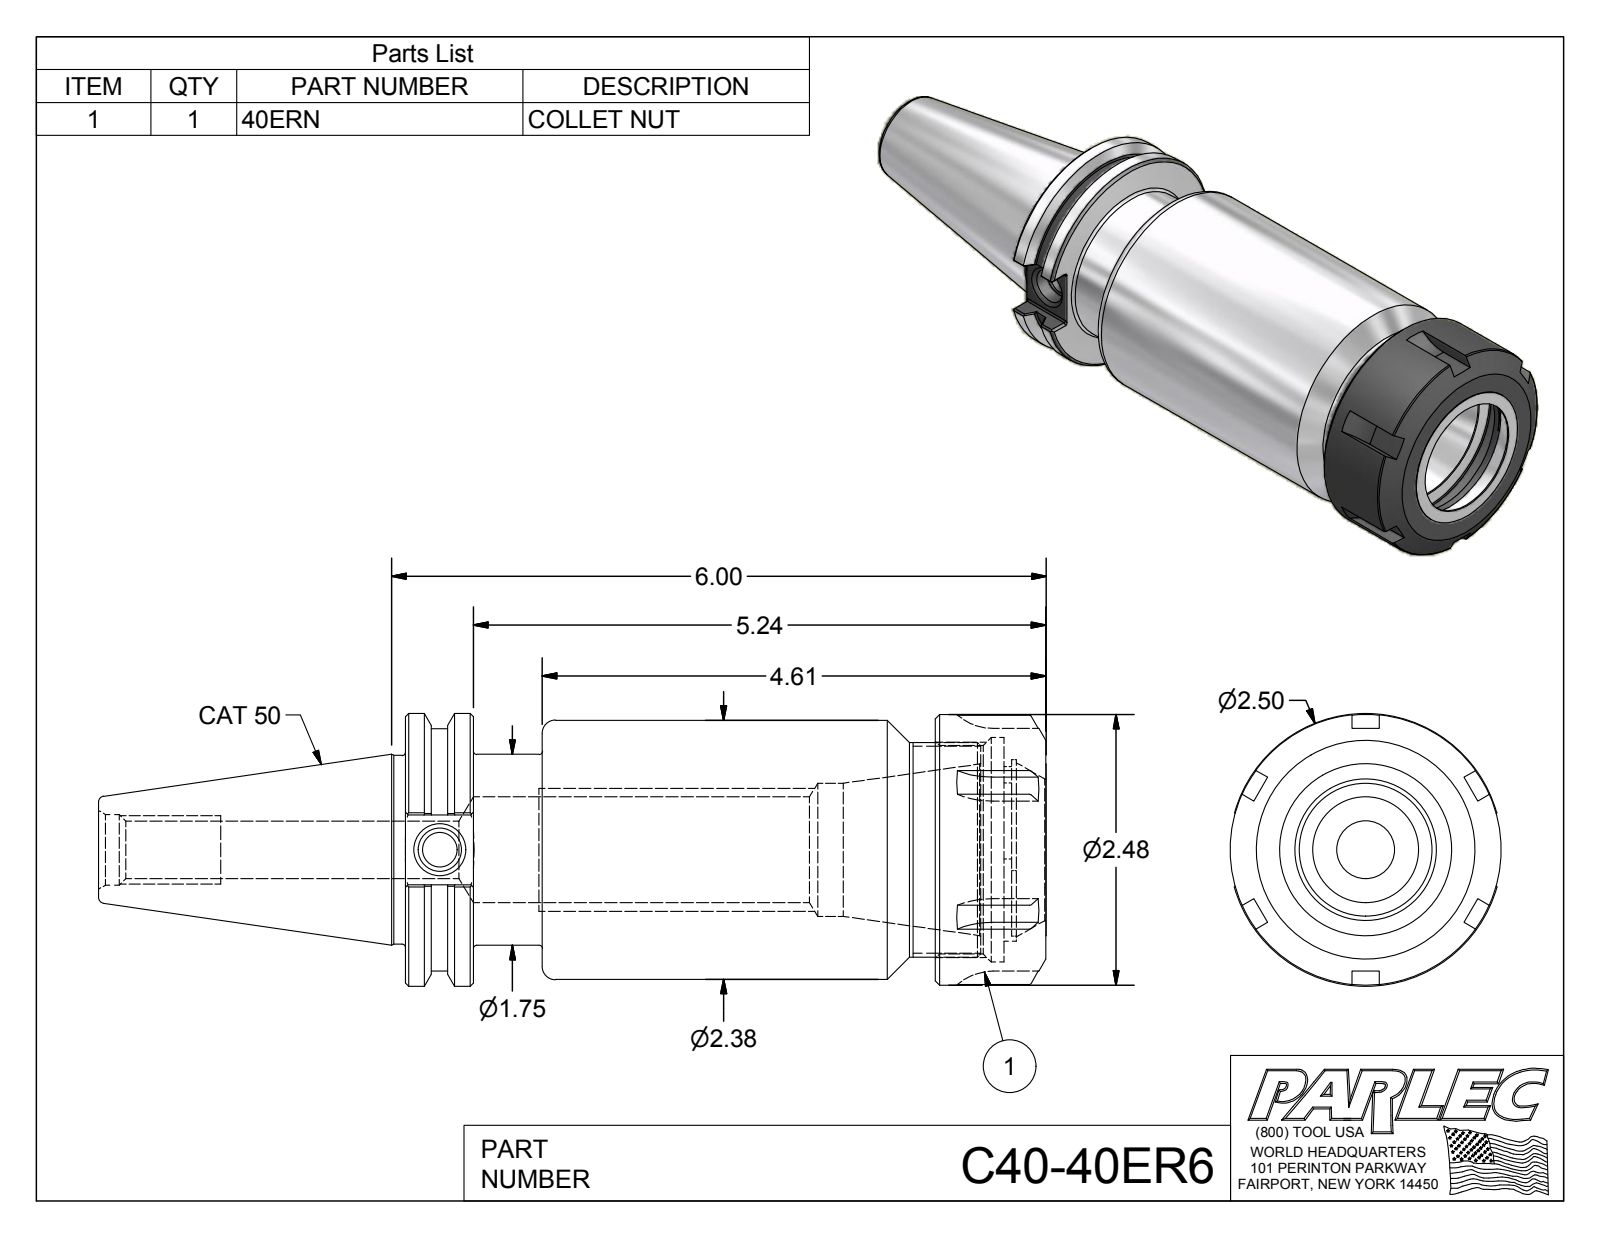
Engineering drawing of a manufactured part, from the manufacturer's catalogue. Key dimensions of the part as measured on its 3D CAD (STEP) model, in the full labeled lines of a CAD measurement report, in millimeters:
Part name (STEP PRODUCT): C40-40ER6; C40-40ER6-1; 40ERN
STEP written by: Autodesk Inventor 2012 (AUTOMOTIVE_DESIGN)
Units: millimetres
Bodies: 2 solids, 142 faces (56 planar, 42 cylindrical, 44 other)
Overall size (bounding box): 220.6 × 63.5 × 63
Volume: 358 400 mm³ · Surface area: 65 940 mm²
Round holes (diameter × count): ⌀8 ×1, ⌀10.1 ×1, ⌀13.4 ×1, ⌀16.5 ×1, ⌀24.6 ×1, ⌀31 ×1, ⌀33 ×1, ⌀48.5 ×1, ⌀52.2 ×1
Round bosses / shafts (diameter × count): ⌀63.5 ×1, ⌀63 ×1, ⌀60.3 ×1, ⌀56.4 ×1, ⌀50 ×1, ⌀44.5 ×1, ⌀43.9 ×1, ⌀40 ×1
Partial cylindrical surfaces — rounded edges, fillets, slot ends (radius × count): R0.5 ×12, R12.7 ×6, R19.4 ×1, R20 ×1, R21 ×1
Main face-to-face distances: 15.9, 123.4, 107.5, 139.4, 123.5, 16, 149.1, 133.2, 25.7, 9.7
